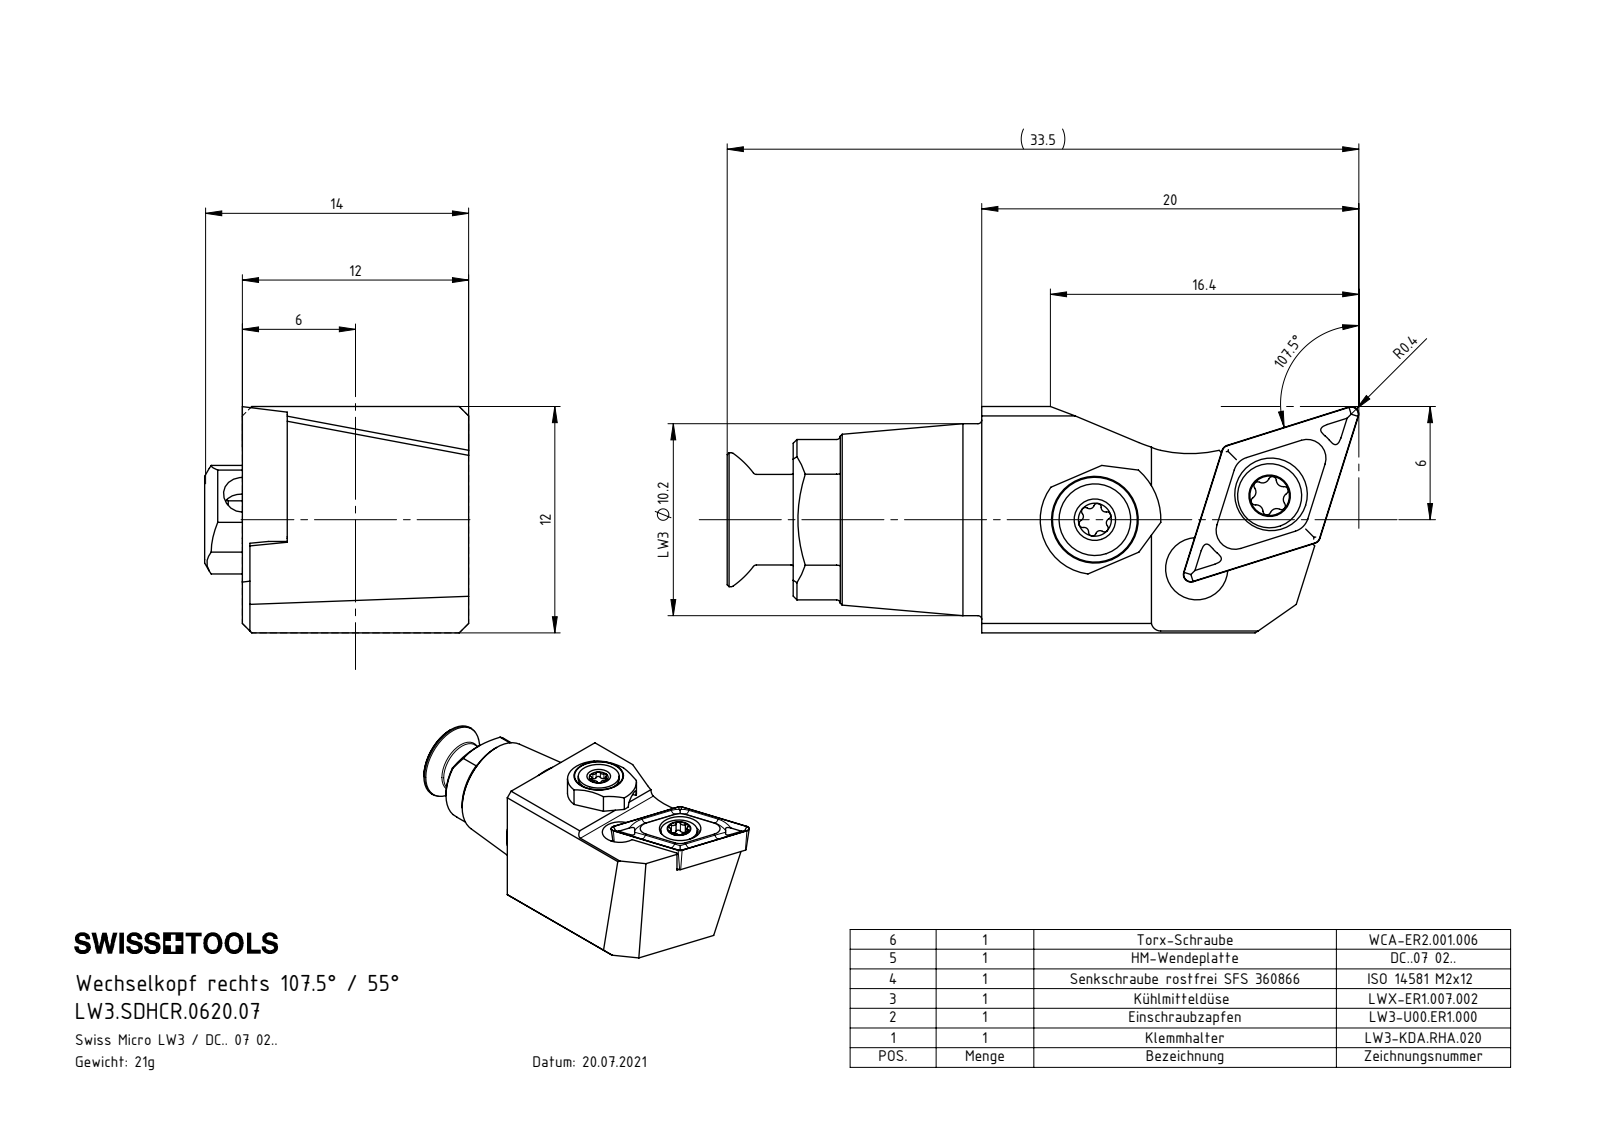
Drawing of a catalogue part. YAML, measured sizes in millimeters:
part_name: "LW3-U00.ER1.000_B; LW3.SDHCR.0620.07; WCA-ER2.001.006_A; ISO 14581 - M2x12 (+3 more)"
step_written_by: "SolidWorks 2022 (CONFIG_CONTROL_DESIGN)"
units: millimeters
bodies: {solids: 6, faces: 254, planar: 71, cylindrical: 79, other: 104}
overall_size: [33.39, 14, 12]
volume: 2731
surface_area: 2352
round_holes:
  - {diameter: 1.6, count: 1}
  - {diameter: 2, count: 1}
  - {diameter: 2.05, count: 1}
  - {diameter: 2.5, count: 1}
  - {diameter: 2.8, count: 1}
  - {diameter: 3, count: 1}
  - {diameter: 3.3, count: 1}
  - {diameter: 3.85, count: 1}
  - {diameter: 5.5, count: 1}
round_bosses_or_shafts:
  - {diameter: 10.18, count: 1}
  - {diameter: 6.9, count: 1}
  - {diameter: 6, count: 1}
  - {diameter: 5, count: 1}
  - {diameter: 4.8, count: 1}
  - {diameter: 3.8, count: 1}
  - {diameter: 3.4, count: 1}
  - {diameter: 2.5, count: 1}
partial_cylinders:
  - {radius: 0.2, count: 8}
  - {radius: 0.21, count: 6}
  - {radius: 0.24, count: 6}
  - {radius: 0.36, count: 4}
  - {radius: 0.36, count: 2}
  - {radius: 0.5, count: 1}
  - {radius: 1, count: 1}
  - {radius: 2.9, count: 1}
face_to_face_distances: [12, 9.62, 2.38, 2, 11.6, 1.98, 0.4, 2.5, 13.4, 11.4]
hole_center_spacings: [5.47, 5.57, 5.99, 9.36, 9.44]
